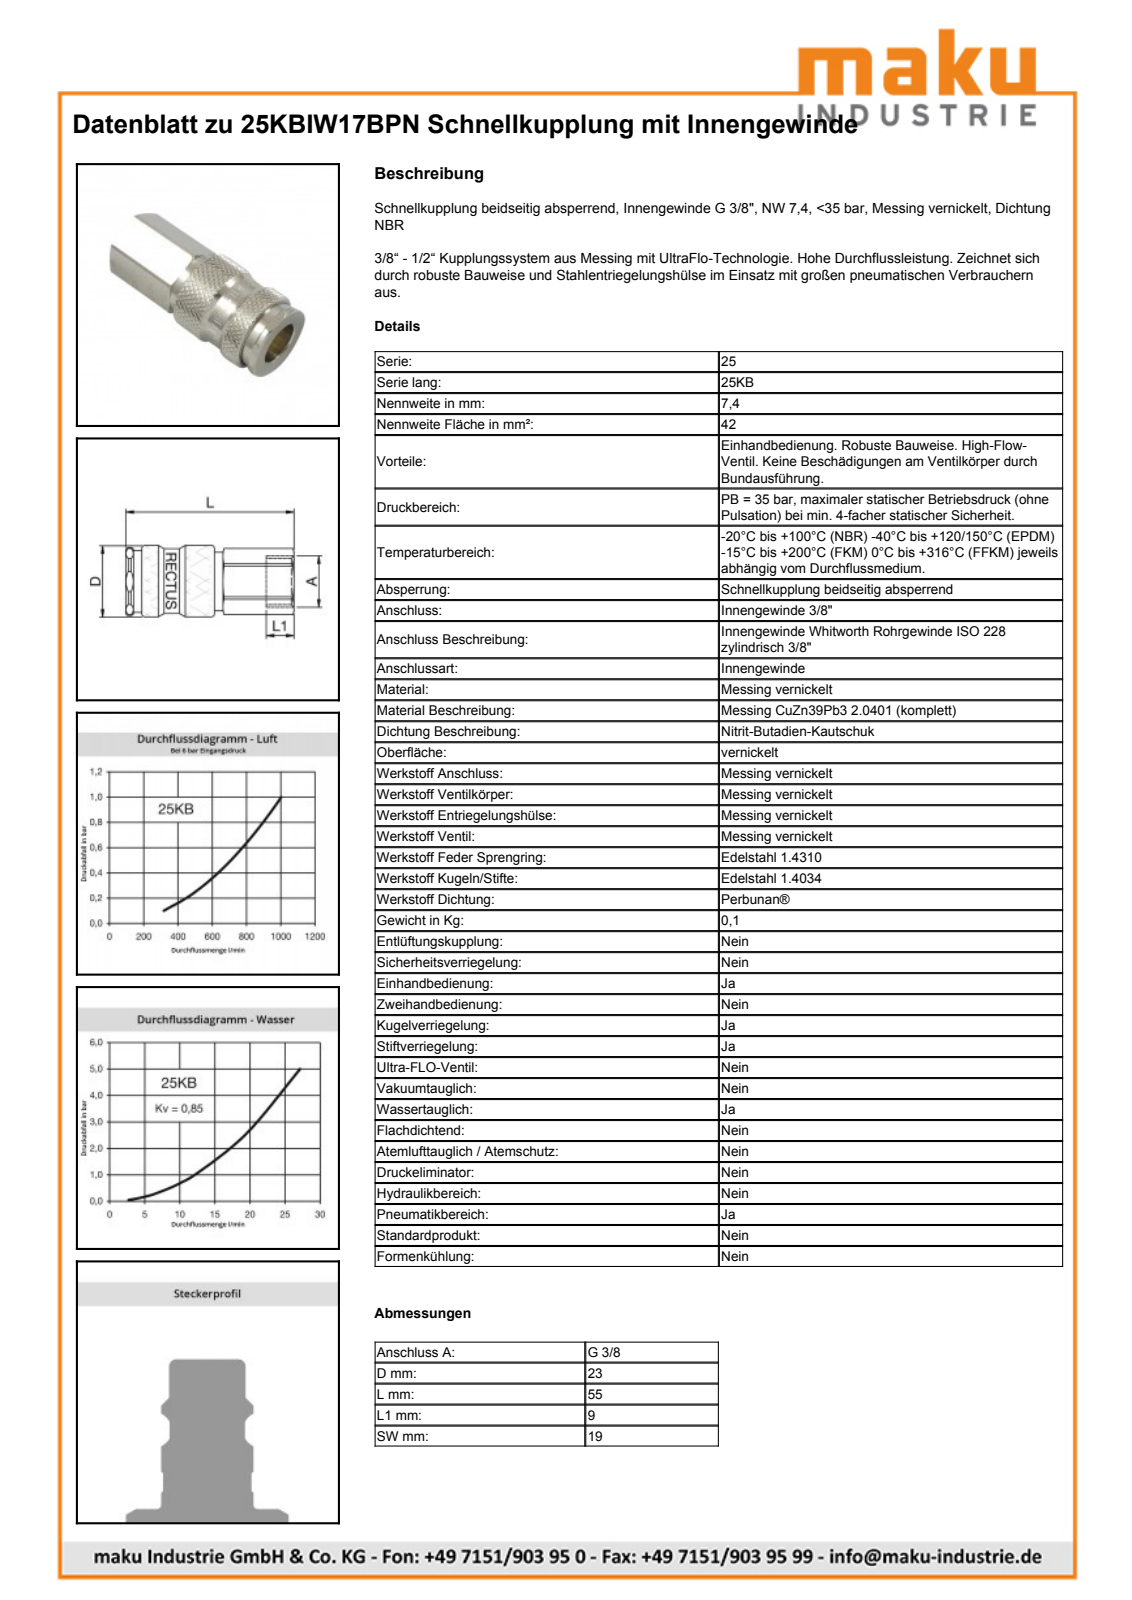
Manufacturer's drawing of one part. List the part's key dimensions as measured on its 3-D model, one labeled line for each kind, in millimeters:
Part name (STEP PRODUCT): D106611
STEP written by: Autodesk Inventor 2013 (AUTOMOTIVE_DESIGN)
Units: millimetres
Bodies: 2 solids, 734 faces (251 planar, 84 cylindrical, 399 other)
Overall size (bounding box): 54.5 × 23.15 × 23.15
Volume: 16 115 mm³ · Surface area: 8 177 mm²
Round holes (diameter × count): ⌀14 ×1, ⌀14.95 ×1, ⌀16 ×1, ⌀17.25 ×1, ⌀19.35 ×1, ⌀20.05 ×1
Round bosses / shafts (diameter × count): ⌀23.15 ×1, ⌀21 ×1, ⌀20 ×1, ⌀18.95 ×1, ⌀15.3 ×1, ⌀15.12 ×1
Partial cylindrical surfaces — rounded edges, fillets, slot ends (radius × count): R7.9 ×1, R10.4 ×1, R10.7 ×1, R11 ×1
Main face-to-face distances: 19, 45.48, 24.5, 20.98, 54.5, 30, 9.02, 21, 28.7, 4.2
